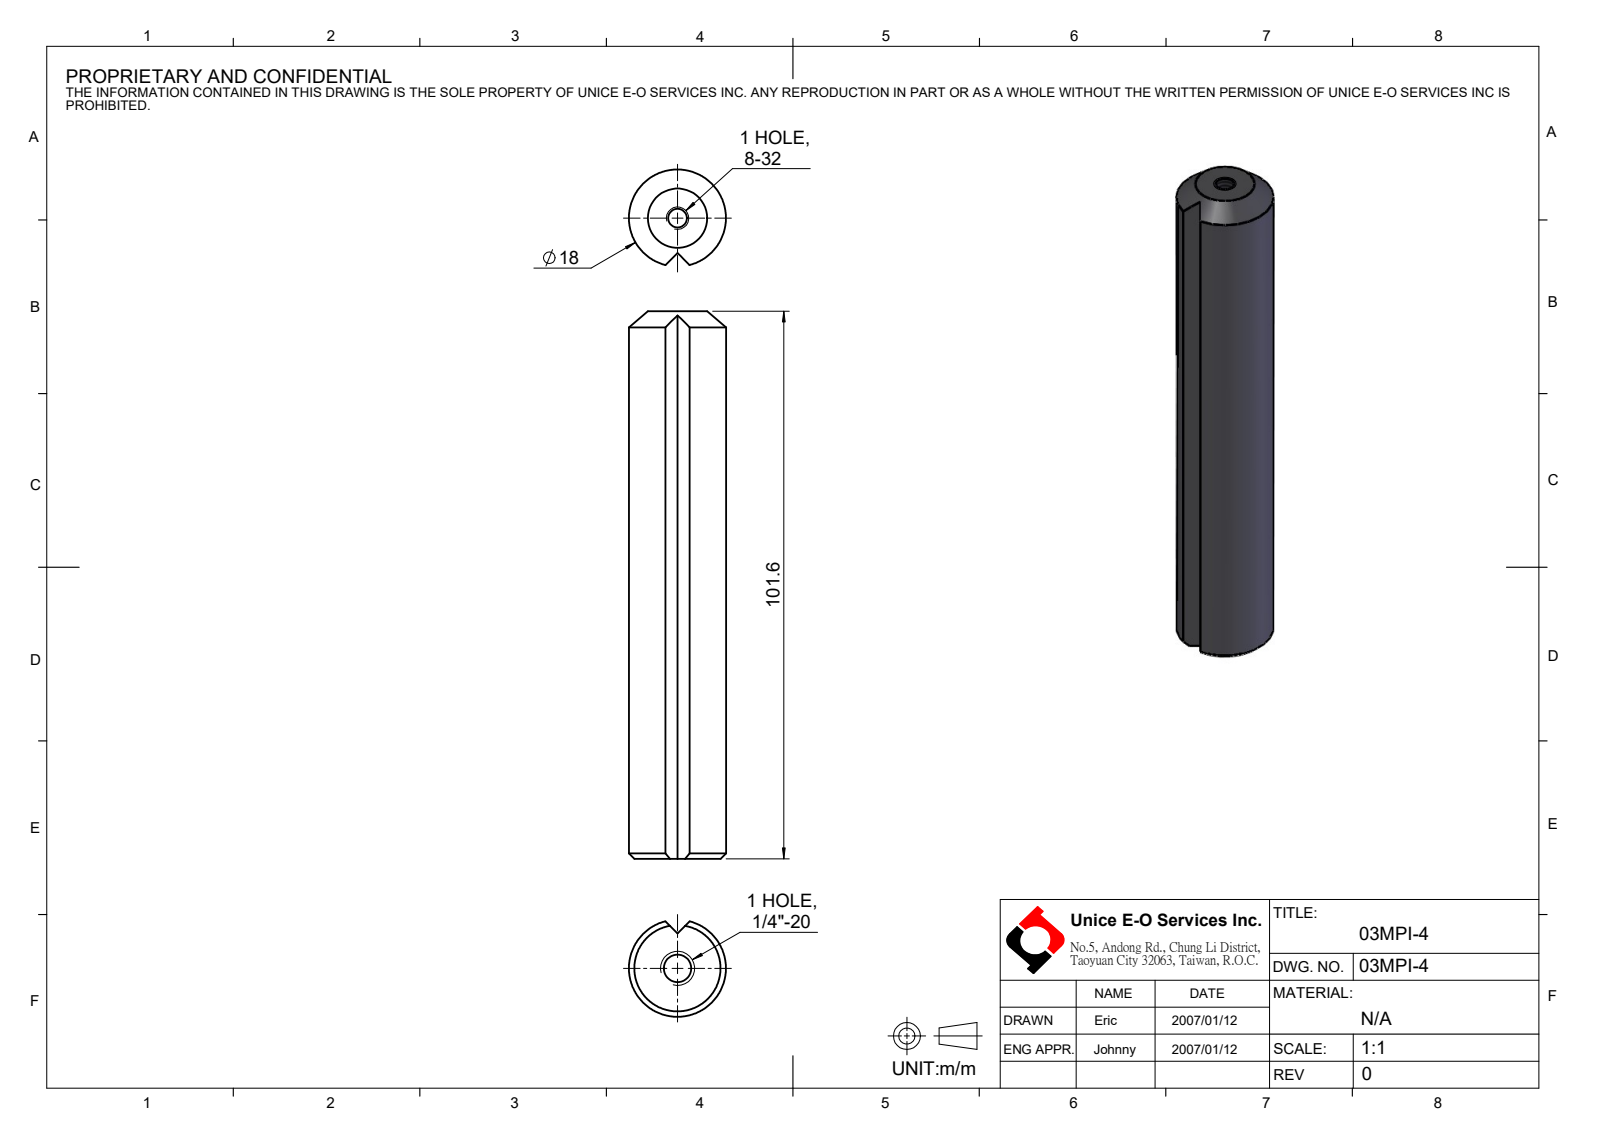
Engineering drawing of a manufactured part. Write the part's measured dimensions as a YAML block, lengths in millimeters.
part_name: "03MPI-4"
step_written_by: "SolidWorks 2016 (CONFIG_CONTROL_DESIGN)"
units: millimeters
bodies: {solids: 1, faces: 20, planar: 4, cylindrical: 7, other: 9}
overall_size: [101.6, 18, 17.71]
volume: 24588
surface_area: 6614
round_holes:
  - {diameter: 3.45, count: 1}
  - {diameter: 5.11, count: 1}
round_bosses_or_shafts:
  - {diameter: 18, count: 1}
face_to_face_distances: [101.6]
